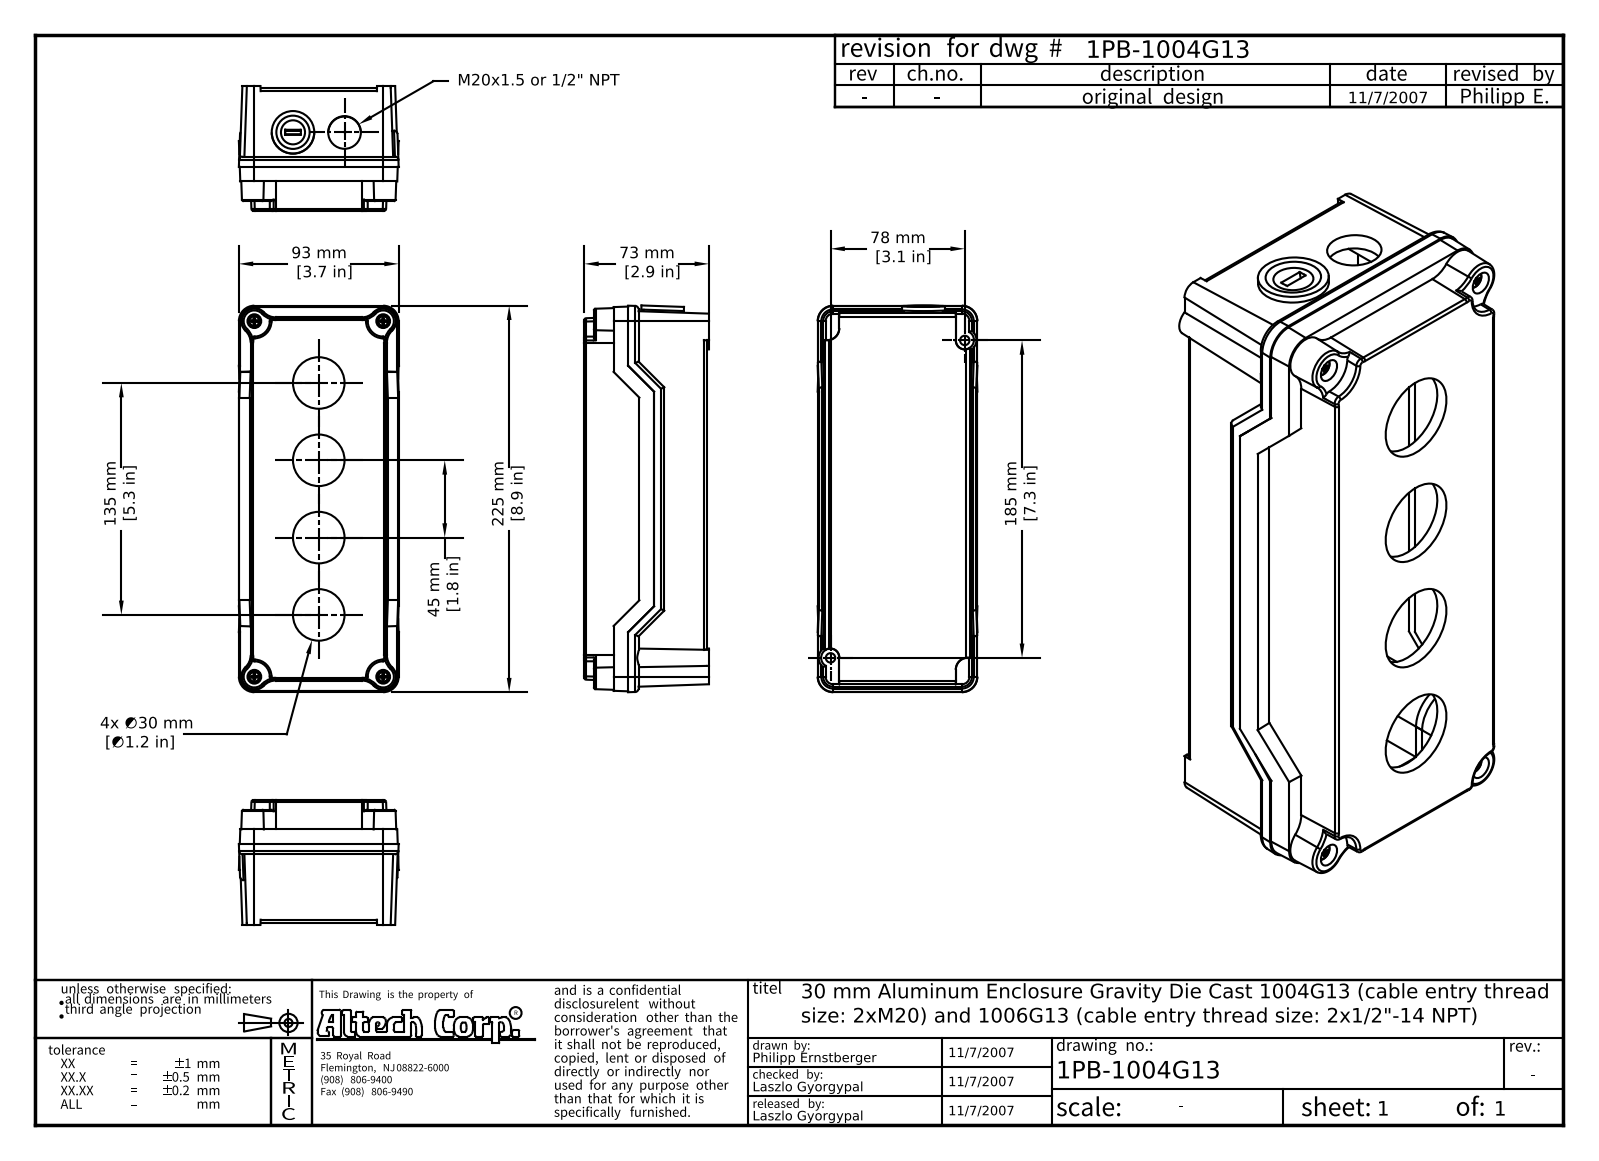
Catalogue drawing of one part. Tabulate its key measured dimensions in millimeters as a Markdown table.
| quantity | value |
| --- | --- |
| part name | 1004G13; enclosure_back; enclosure_front; DIN 125-1 B B 4 (+4 more) |
| STEP written by | Autodesk Inventor 2008 (AUTOMOTIVE_DESIGN) |
| units | millimeters |
| bodies | 12 solids, 515 faces (204 planar, 77 cylindrical, 234 other) |
| overall size | 225.13 × 93 × 72.5 |
| volume | 413 798 mm³ |
| surface area | 165 670 mm² |
| round holes (diameter × count) | 3.5 × 4, 30 × 4, 4.3 × 2, 19 × 2 |
| round bosses / shafts (diameter × count) | 3.18 × 4, 9 × 2, 4 × 2, 3.62 × 2, 24.75 × 1 |
| partial cylindrical surfaces (radius × count) | 2 × 22, 9 × 6, 1 × 4, 6 × 2, 8.5 × 2, 11.5 × 2, 12 × 2, 7.75 × 1 |
| main face-to-face distances | 6, 65.5, 71.5, 67, 4.5, 61, 74, 40, 25.5, 21 |
| hole center spacings | 51.98, 89.26, 131.46, 175.06, 45, 30.51, 33.51, 60.59 |
